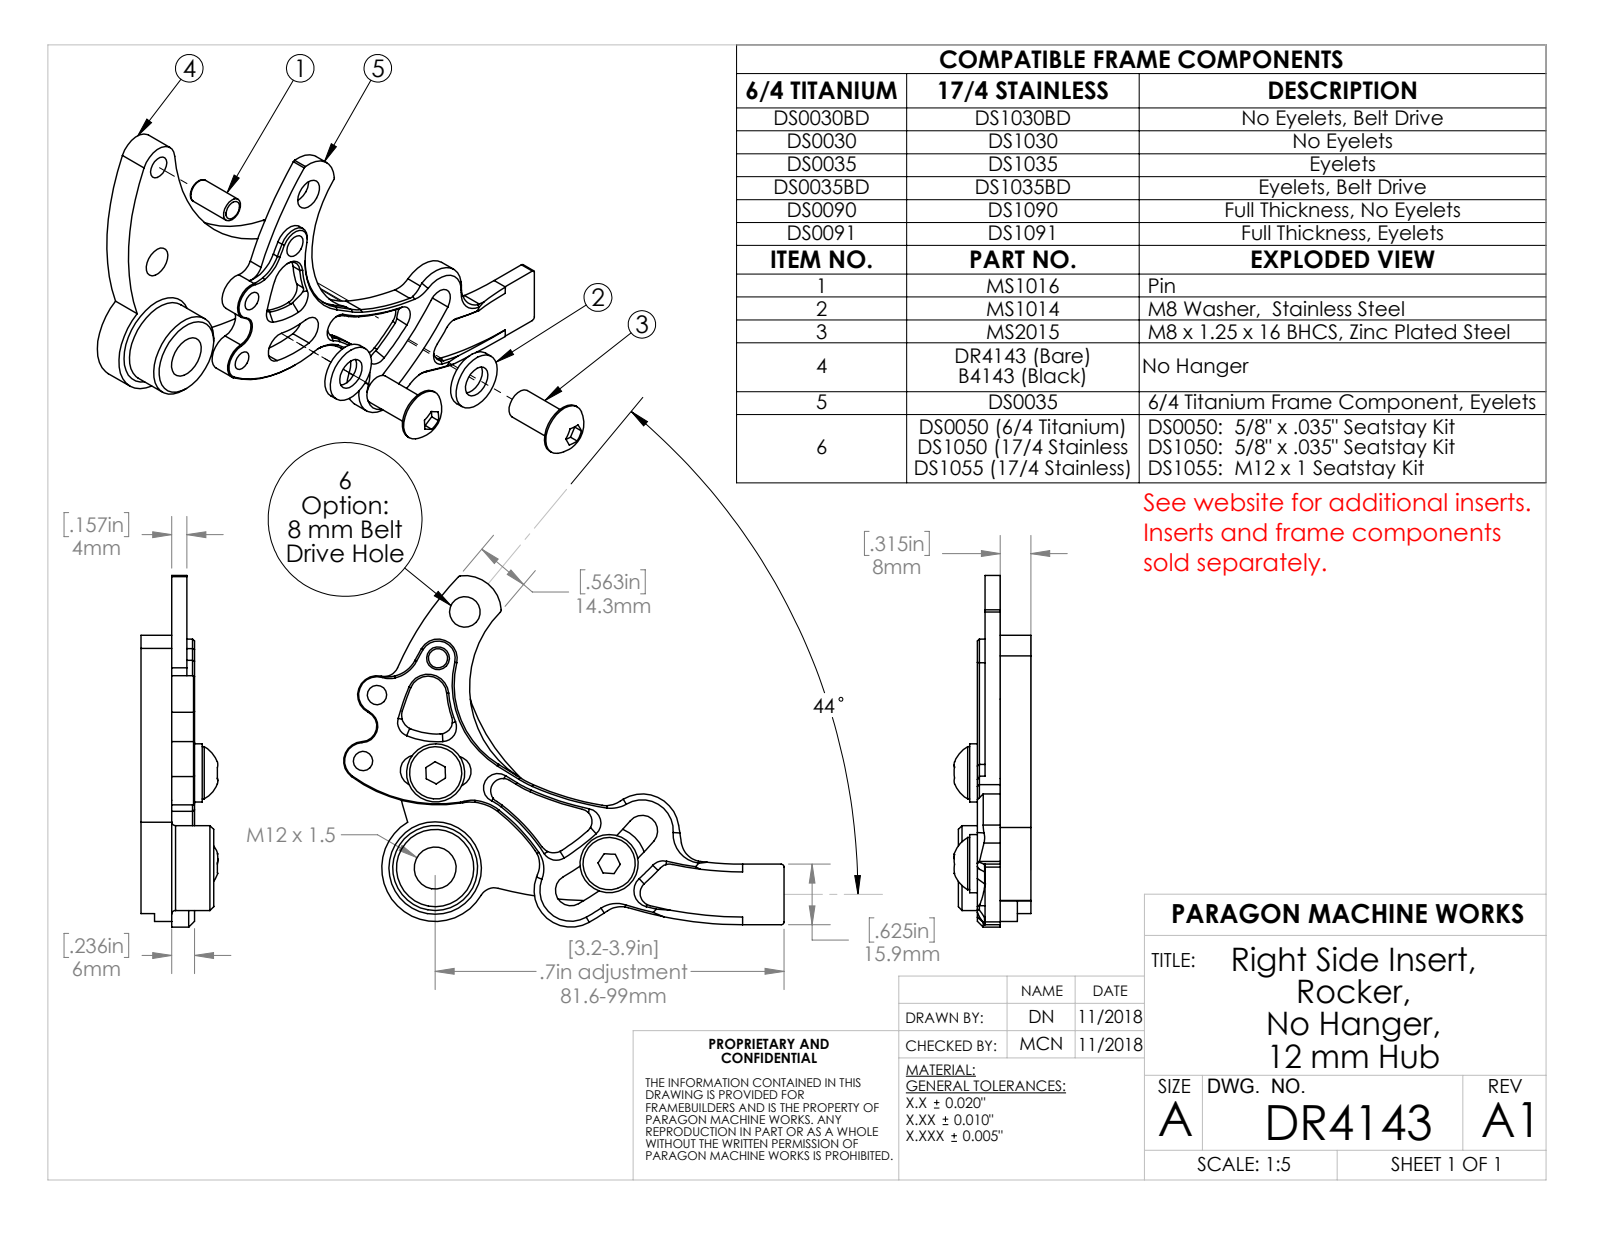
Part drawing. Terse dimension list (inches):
name: DR4143; DR4043; MS2015; ROCKER_PIN (+2 more)
written by: SolidWorks 2018 (AUTOMOTIVE_DESIGN)
unit: in
bodies: 7 solids, 244 faces (49 planar, 129 cylindrical, 66 other)
size: 4.606 × 4.542 × 3.624
volume: 2.038 in³; area: 32.32 in²
holes: 2× ⌀0.2, 2× ⌀0.327, 1× ⌀0.236, 1× ⌀0.315, 1× ⌀0.315, 1× ⌀0.316, 1× ⌀0.433, 1× ⌀0.477
bosses: 2× ⌀0.6, 2× ⌀0.539, 1× ⌀0.875, 1× ⌀0.315, 1× ⌀0.25
rounds: 5× R0.15, 5× R0.16, 4× R0.03, 3× R0.25, 3× R0.38, 2× R0.13, 2× R0.199, 1× R0.125
face distances: 1.752, 0.315, 2.067, 0.138, 0.177, 2.047, 2.303, 1.988, 0.236, 1.89
hole spacings: 0.103, 0.552, 0.695, 0.735, 0.759, 0.981, 1.004, 1.181
